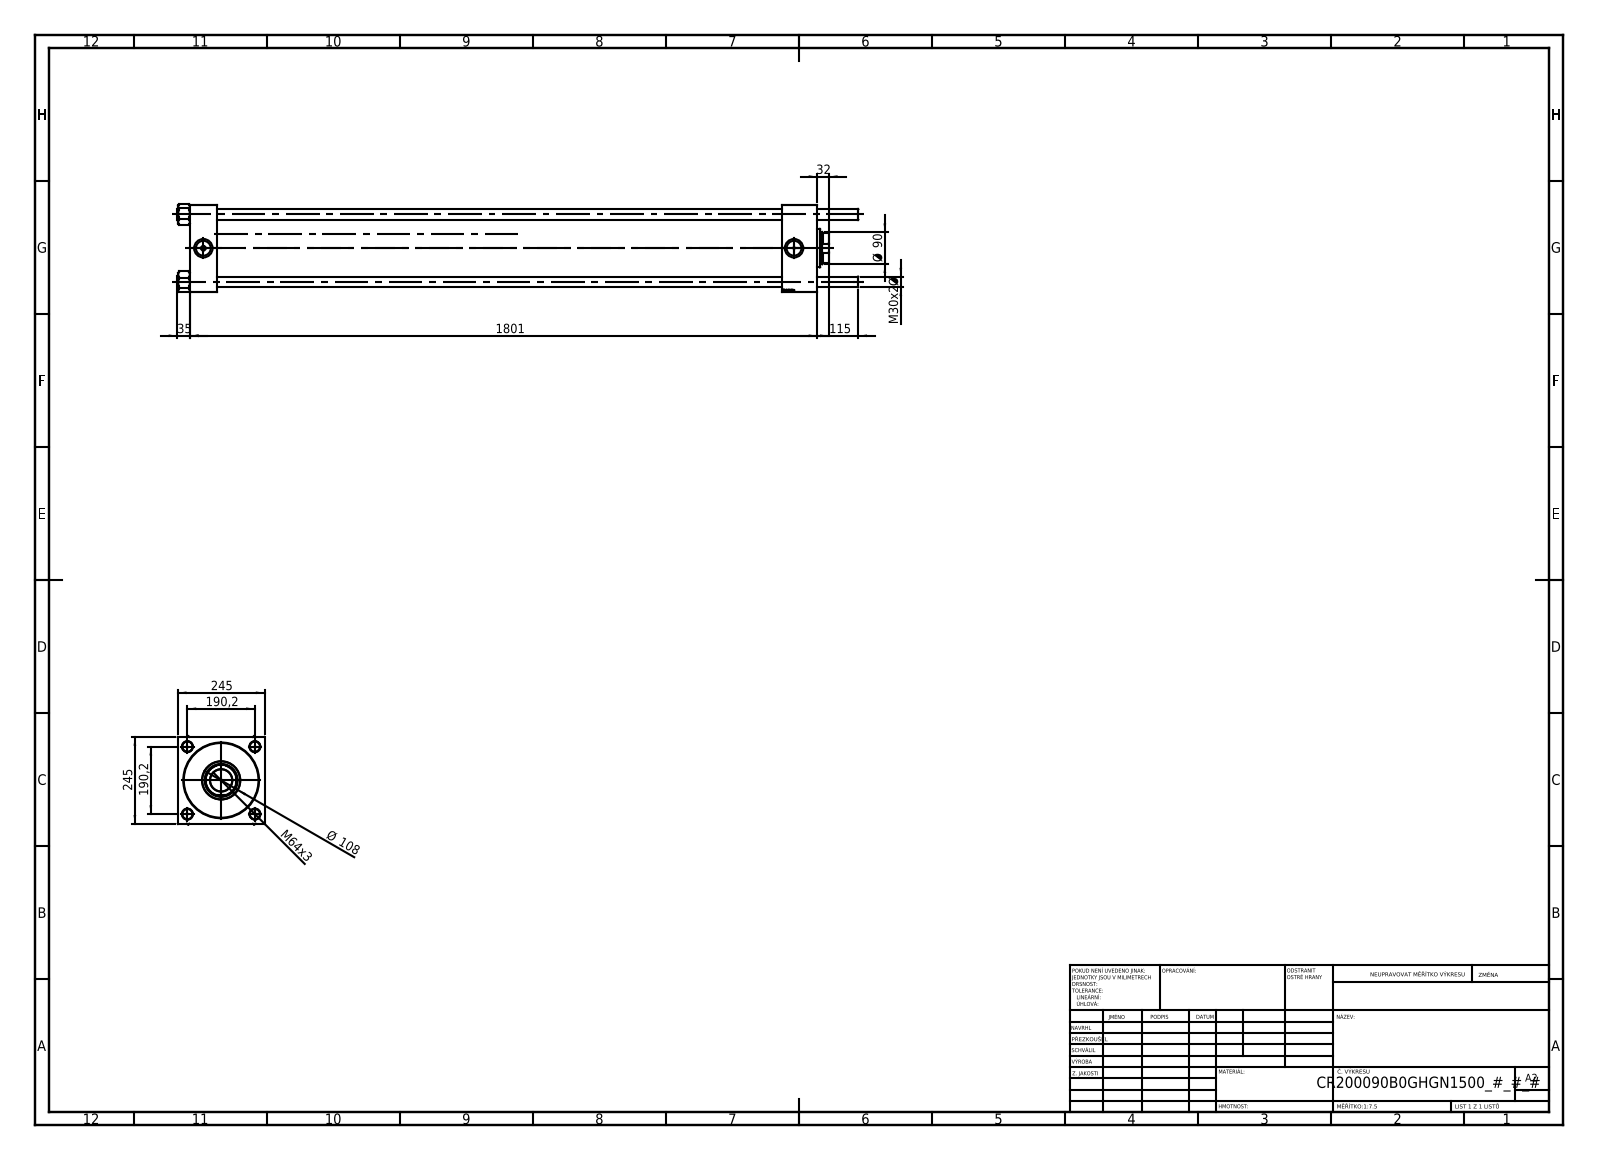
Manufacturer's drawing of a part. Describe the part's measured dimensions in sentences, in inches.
The part is named "NUT_M5_B; V215CR_VCP_B; V215CR_B_TYCINKA; V215_VC_A (+1 more)". Its 3-D file was written by "SolidWorks 2019 (CONFIG_CONTROL_DESIGN)". It is 11 solids with 1206 faces: 480 planar, 78 cylindrical and 648 other. Overall it measures 75.551 by 9.812 by 9.646 inches. Its volume is 1 853 cubic inches and its surface area 6 178 square inches. Round holes: 4 of diameter 1.181, 2 of diameter 0.276, 2 of diameter 1.65, 2 of diameter 2.047, 1 of diameter 2.461, 1 of diameter 3.543, 1 of diameter 3.661, 1 of diameter 5.748, 1 of diameter 7.874, 1 of diameter 8.287. Round bosses or shafts: 4 of diameter 1.299, 1 of diameter 8.11, 1 of diameter 4.252. Partial cylindrical surfaces (rounded edges, fillets, slot ends): 1 of radius 1.732. The main face-to-face distances are 9.646, 2.992, 69.646, 66.654, 68.516, 65.524, 1.13, 3.976, 65.669, 62.677. The hole center spacings are 5.295, 7.488, 10.59, 65.551.
